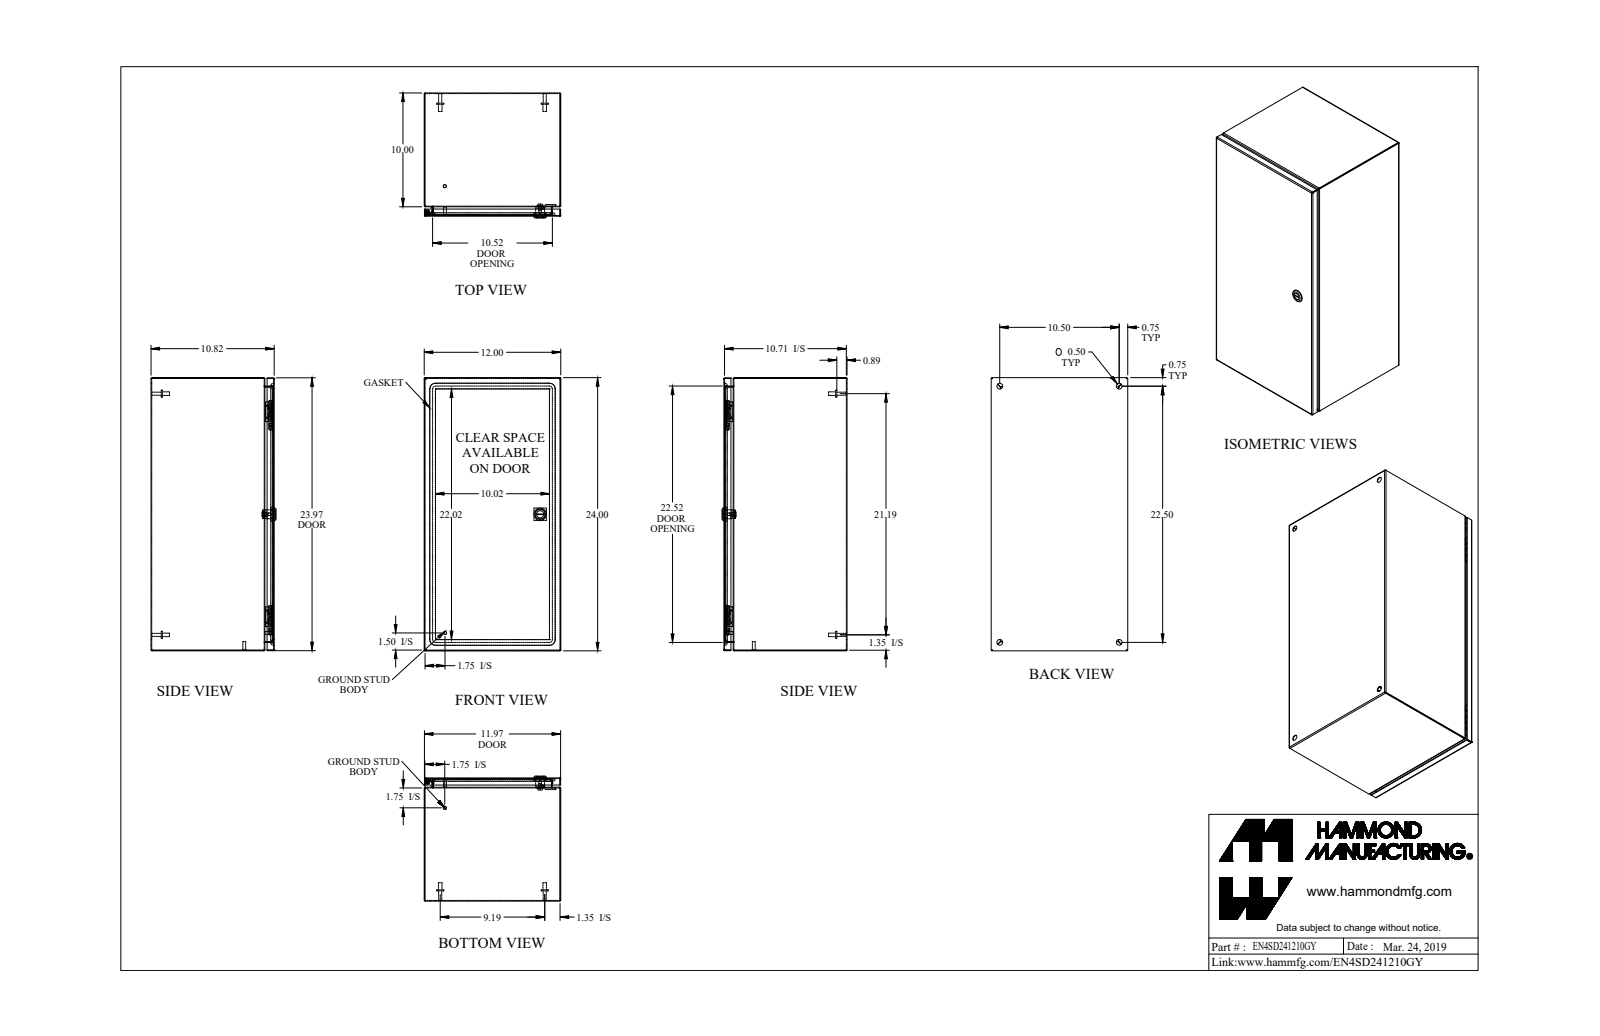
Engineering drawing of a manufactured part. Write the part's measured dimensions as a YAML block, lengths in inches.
part_name: "EN4SD241210GY_Default"
step_written_by: "SolidWorks 2019 (CONFIG_CONTROL_DESIGN)"
units: inches
bodies: {solids: 21, faces: 634, planar: 285, cylindrical: 213, other: 136}
overall_size: [24, 12, 10.982]
volume: 88.95
surface_area: 3031
round_holes:
  - {diameter: 0.5, count: 4}
  - {diameter: 0.172, count: 1}
  - {diameter: 0.232, count: 1}
  - {diameter: 0.24, count: 1}
  - {diameter: 0.242, count: 1}
  - {diameter: 0.625, count: 1}
  - {diameter: 0.785, count: 1}
round_bosses_or_shafts:
  - {diameter: 0.625, count: 4}
  - {diameter: 0.313, count: 4}
  - {diameter: 0.27, count: 4}
  - {diameter: 0.281, count: 2}
  - {diameter: 0.25, count: 2}
  - {diameter: 1.1, count: 1}
  - {diameter: 0.525, count: 1}
  - {diameter: 0.455, count: 1}
partial_cylinders:
  - {radius: 0.029, count: 21}
  - {radius: 0.086, count: 21}
  - {radius: 0.25, count: 16}
  - {radius: 19, count: 8}
  - {radius: 0.006, count: 4}
  - {radius: 0.062, count: 4}
  - {radius: 0.499, count: 4}
  - {radius: 0.125, count: 2}
face_to_face_distances: [0.057, 10.765, 11.943, 10.708, 10.822, 11.886, 12, 23.943, 23.886, 24]
hole_center_spacings: [10.5, 22.5, 24.83, 11.299, 11.3, 14.686, 14.687]
